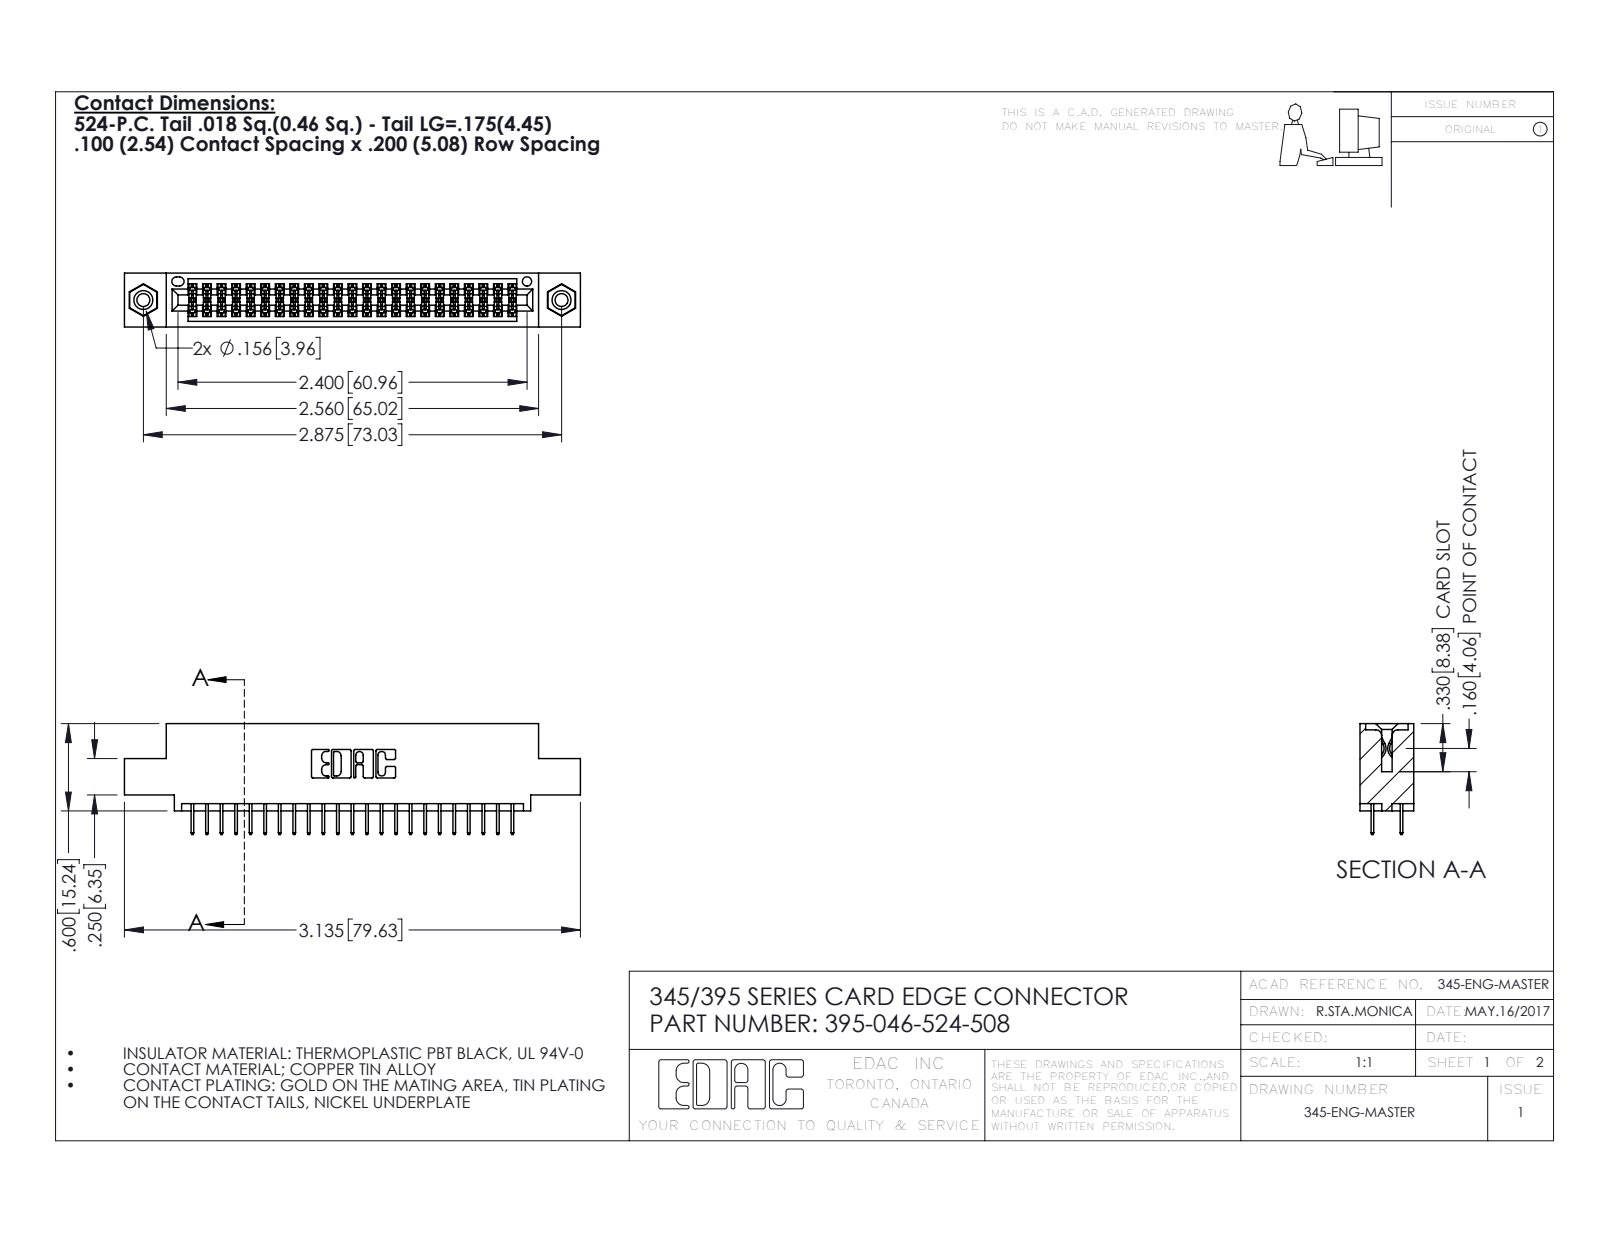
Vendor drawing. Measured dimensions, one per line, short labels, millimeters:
name: 345-292-001_345-293-124; 395-046-524-508; 345 Part_0.110 Offset - 0.156 Dia-TI; 345-250-001_345-250-003-102
written by: SolidWorks 2016 (CONFIG_CONTROL_DESIGN)
unit: mm
bodies: 49 solids, 2674 faces (1910 planar, 748 cylindrical, 16 other)
size: 79.6 × 19.4 × 9.4
volume: 7 410 mm³; area: 10 510 mm²
holes: 2× ⌀2.3, 2× ⌀3.2, 2× ⌀4, 1× ⌀1.6
bosses: 2× ⌀3.9
rounds: 69× R0.2, 22× R0.3, 6× R0.2, 6× R0.8, 3× R0.7, 2× R0.4, 2× R0.5, 2× R0.6
face distances: 1.8, 7.6, 5.1, 9.4, 2.5, 6.9, 0.6, 5.7, 1.8, 4.4
hole spacings: 6.9, 67.1, 73
